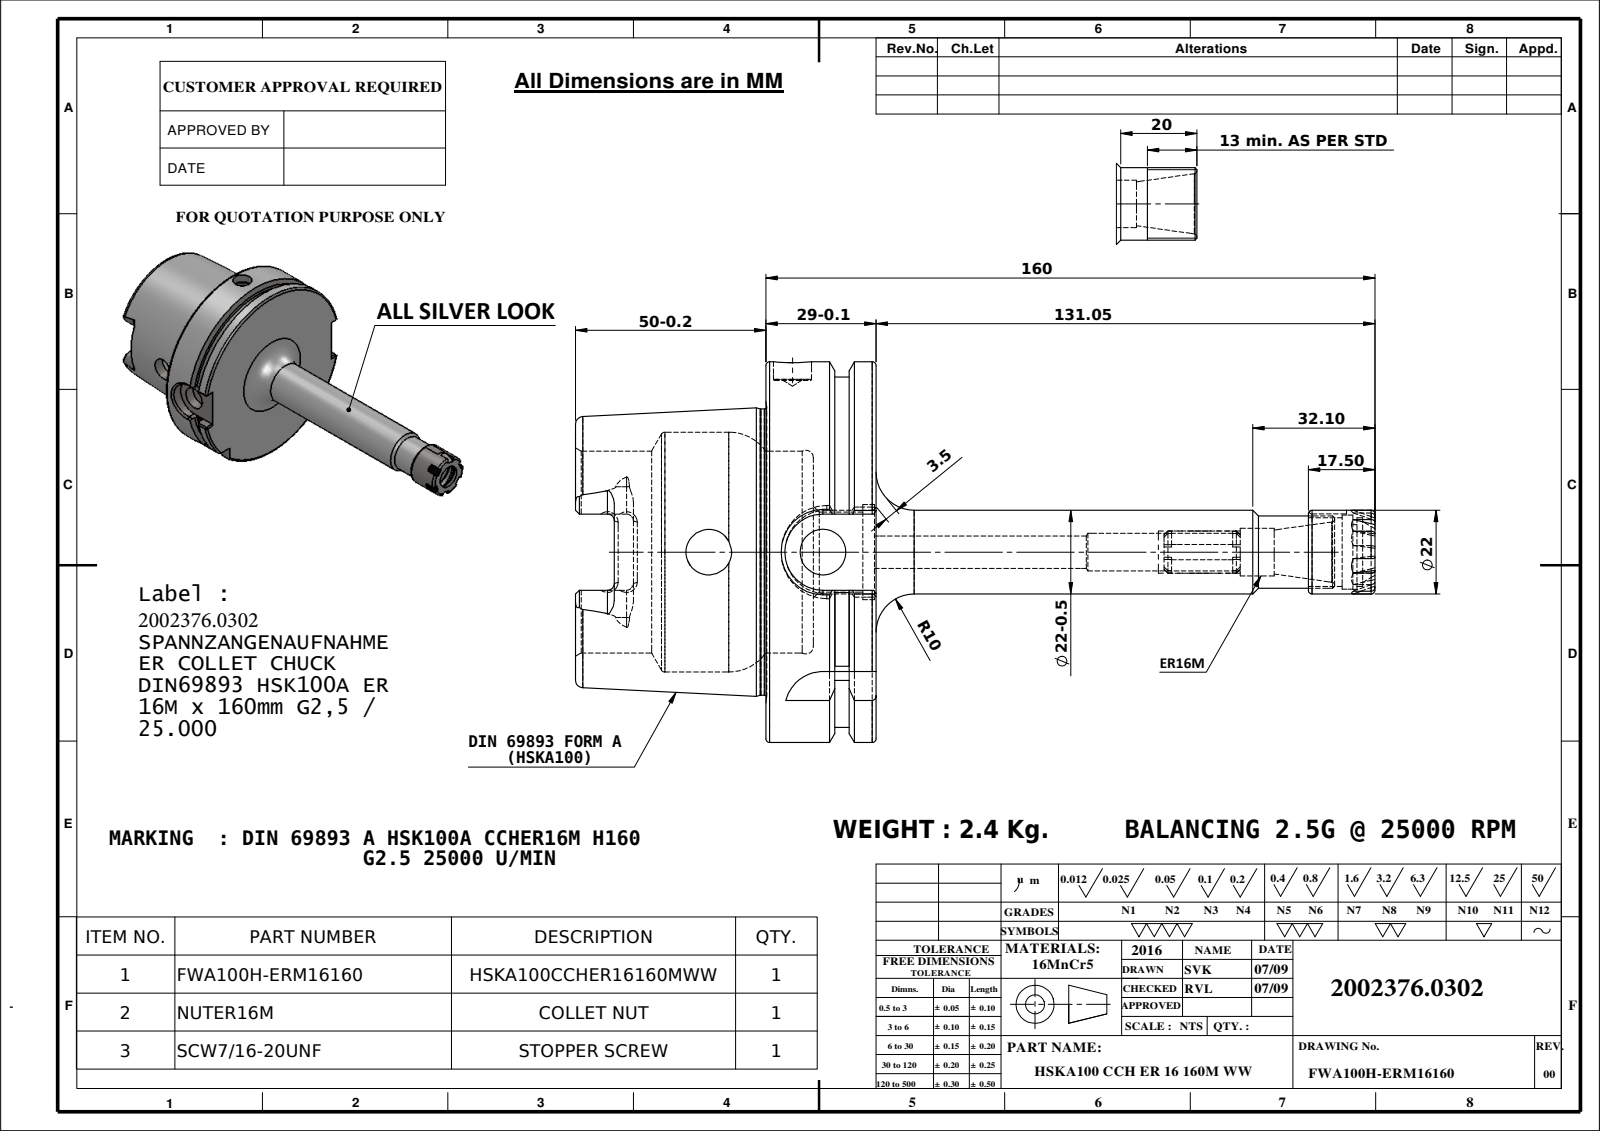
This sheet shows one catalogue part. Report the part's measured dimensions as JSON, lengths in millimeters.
{"part_name": "FTNUTER16M; 91100A-ERM16160; HSKA100CCHER16160MWW; FTSCW71620", "step_written_by": "SolidWorks 2009 (CONFIG_CONTROL_DESIGN)", "units": "millimeters", "bodies": {"solids": 3, "faces": 256, "planar": 98, "cylindrical": 68, "other": 90}, "overall_size": [210, 100, 100], "volume_mm3": 293245, "surface_area_mm2": 65175, "round_holes": [[12, 2], [4, 1], [8.5, 1], [9.92, 1], [10, 1], [12.5, 1], [17, 1], [18, 1], [19.5, 1], [21, 1], [25, 1], [53, 1]], "round_bosses_or_shafts": [[100, 1], [92, 1], [75.16, 1], [22, 1], [19, 1], [11.1, 1]], "partial_cylinders_radius": [[1.8, 6], [4.88, 4], [10, 2], [11, 1]], "face_to_face_distances": [28.95, 16.45, 12.5, 78.95, 62.5, 50, 0.45, 16, 28.5, 78.5], "hole_center_spacings": [1.3, 30]}
